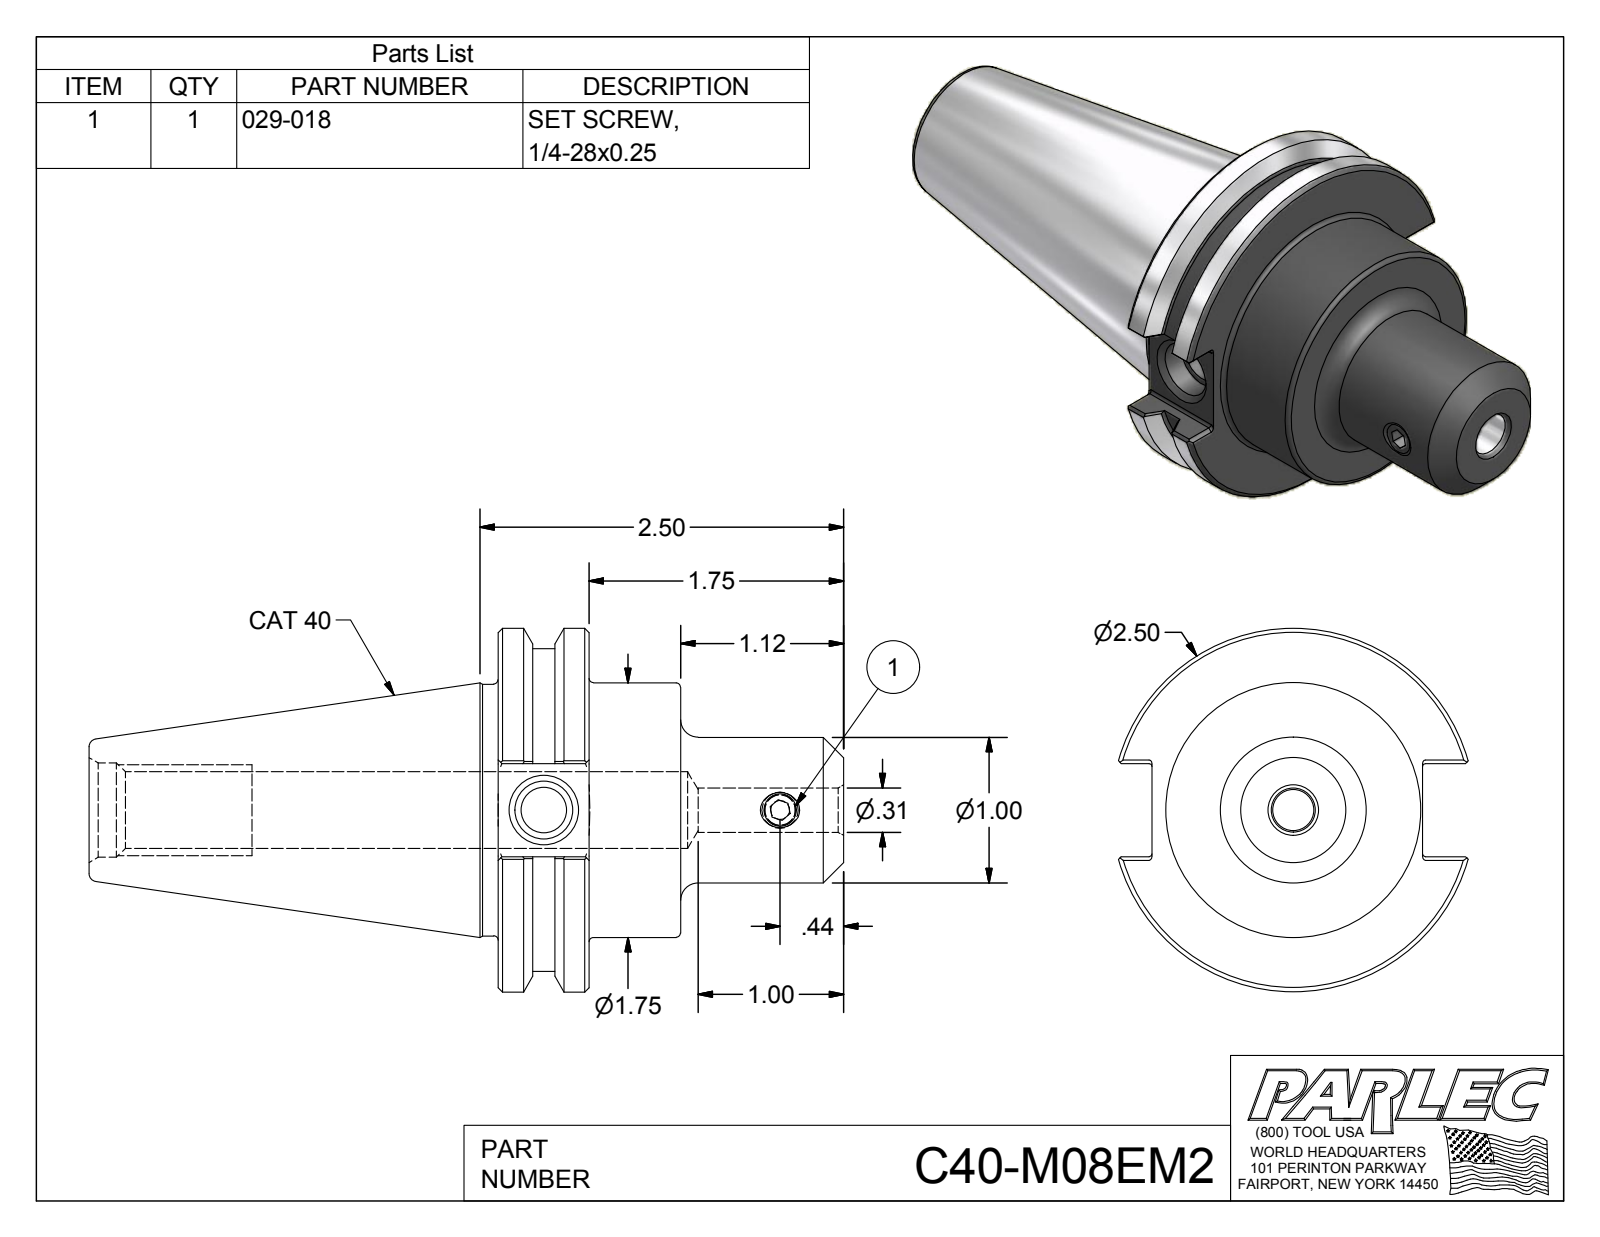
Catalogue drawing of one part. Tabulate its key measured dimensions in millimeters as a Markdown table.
| quantity | value |
| --- | --- |
| part name | C40-M08EM2; C40-M08EM2-1; 029-018 |
| STEP written by | Autodesk Inventor 2012 (AUTOMOTIVE_DESIGN) |
| units | millimeters |
| bodies | 2 solids, 103 faces (42 planar, 28 cylindrical, 33 other) |
| overall size | 131.7 × 63.5 × 61.1 |
| volume | 135 500 mm³ |
| surface area | 26 160 mm² |
| round holes (diameter × count) | 5.4 × 1, 7.7 × 1, 8 × 1, 10.1 × 1, 13.4 × 1, 16.5 × 1 |
| round bosses / shafts (diameter × count) | 63.5 × 1, 56.4 × 1, 44.5 × 1, 43.9 × 1, 25.4 × 1, 6.4 × 1 |
| partial cylindrical surfaces (radius × count) | 0.5 × 12 |
| main face-to-face distances | 15.9, 31.9, 16, 60.3, 44.5, 28.4, 16.3, 47.2, 71.4, 87.3 |
| hole center spacings | 41.2 |
